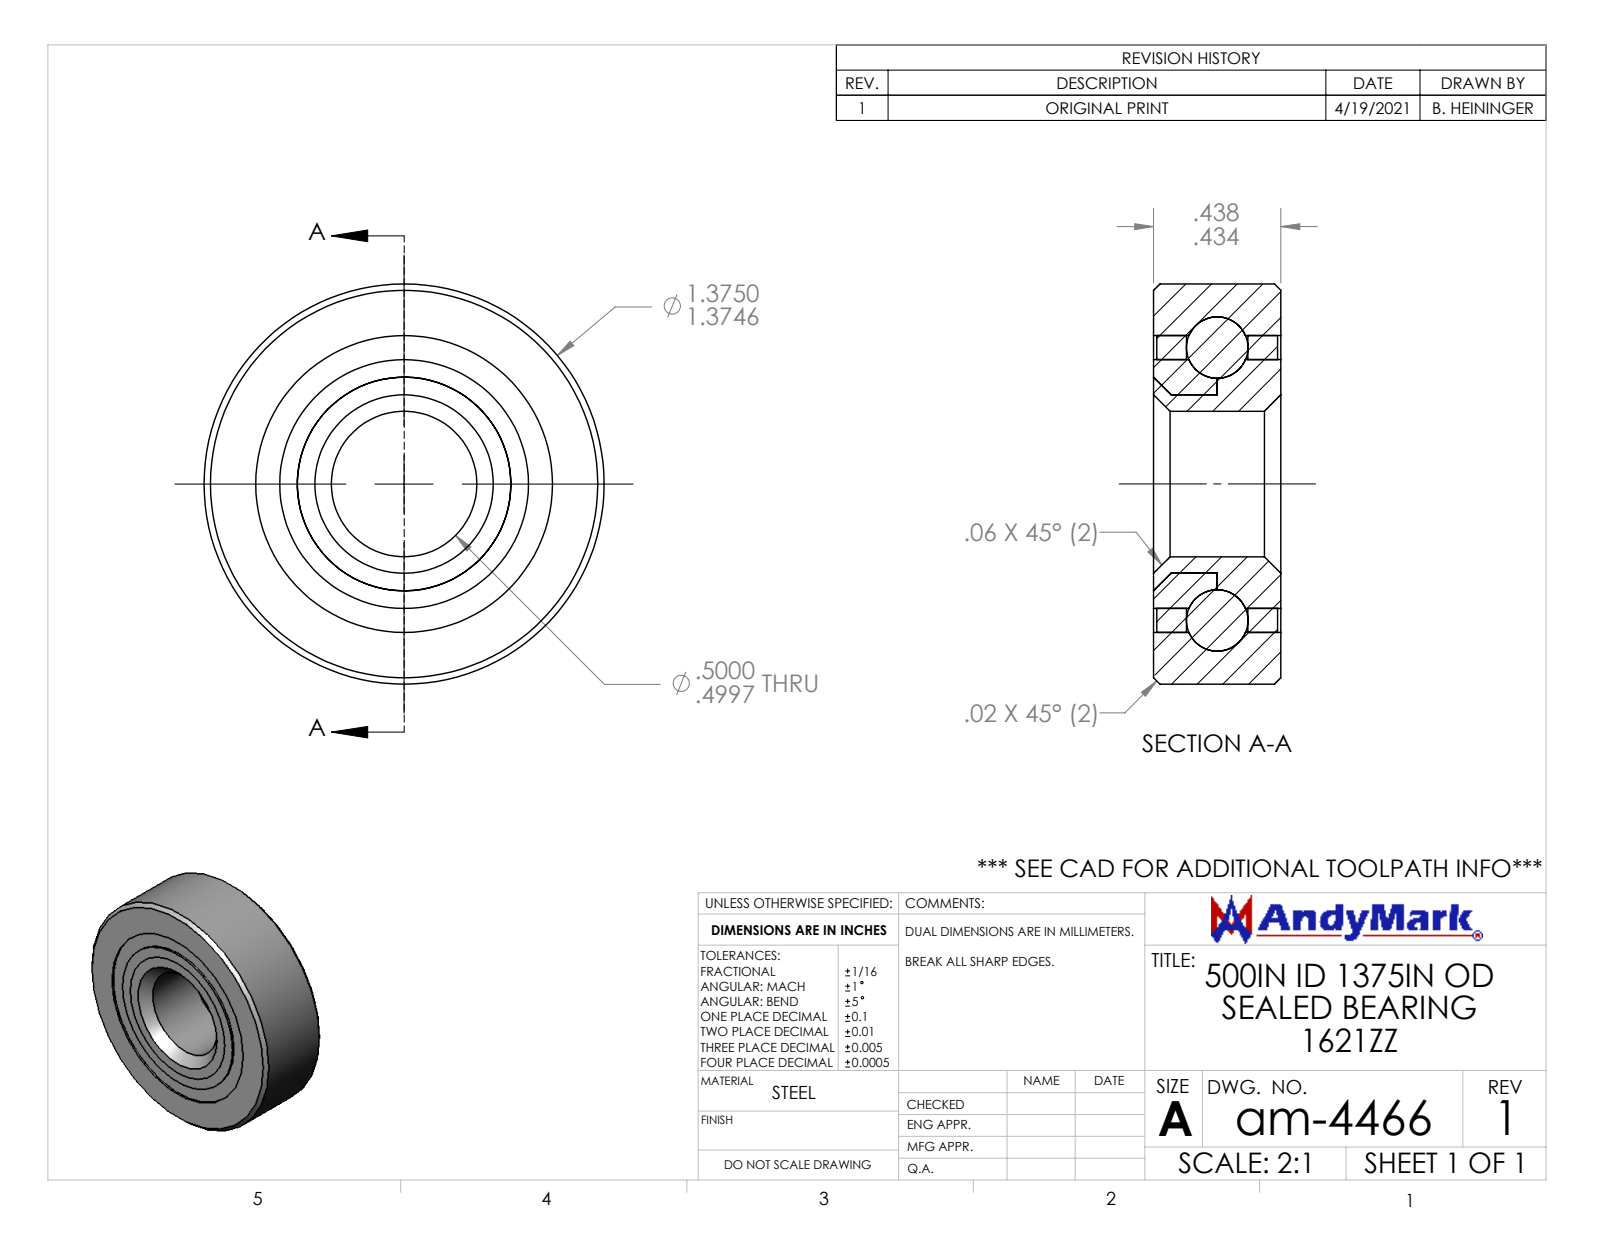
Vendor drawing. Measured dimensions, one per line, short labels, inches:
name: am-4466 1-2 in ID 1 3-8 in OD Sealed Bearing 1621ZZ
written by: SolidWorks 2019 (AUTOMOTIVE_DESIGN)
unit: in
bodies: 15 solids, 73 faces (11 planar, 24 cylindrical, 38 other)
size: 1.375 × 1.375 × 0.438
volume: 0.496 in³; area: 12.13 in²
holes: 1× ⌀0.5, 1× ⌀0.613, 1× ⌀0.855, 1× ⌀1.02
bosses: 1× ⌀1.375
face distances: 0.438, 0.427, 0.113, 0.324, 0.102, 0.313, 0.219, 0.208, 0.106, 0.416
